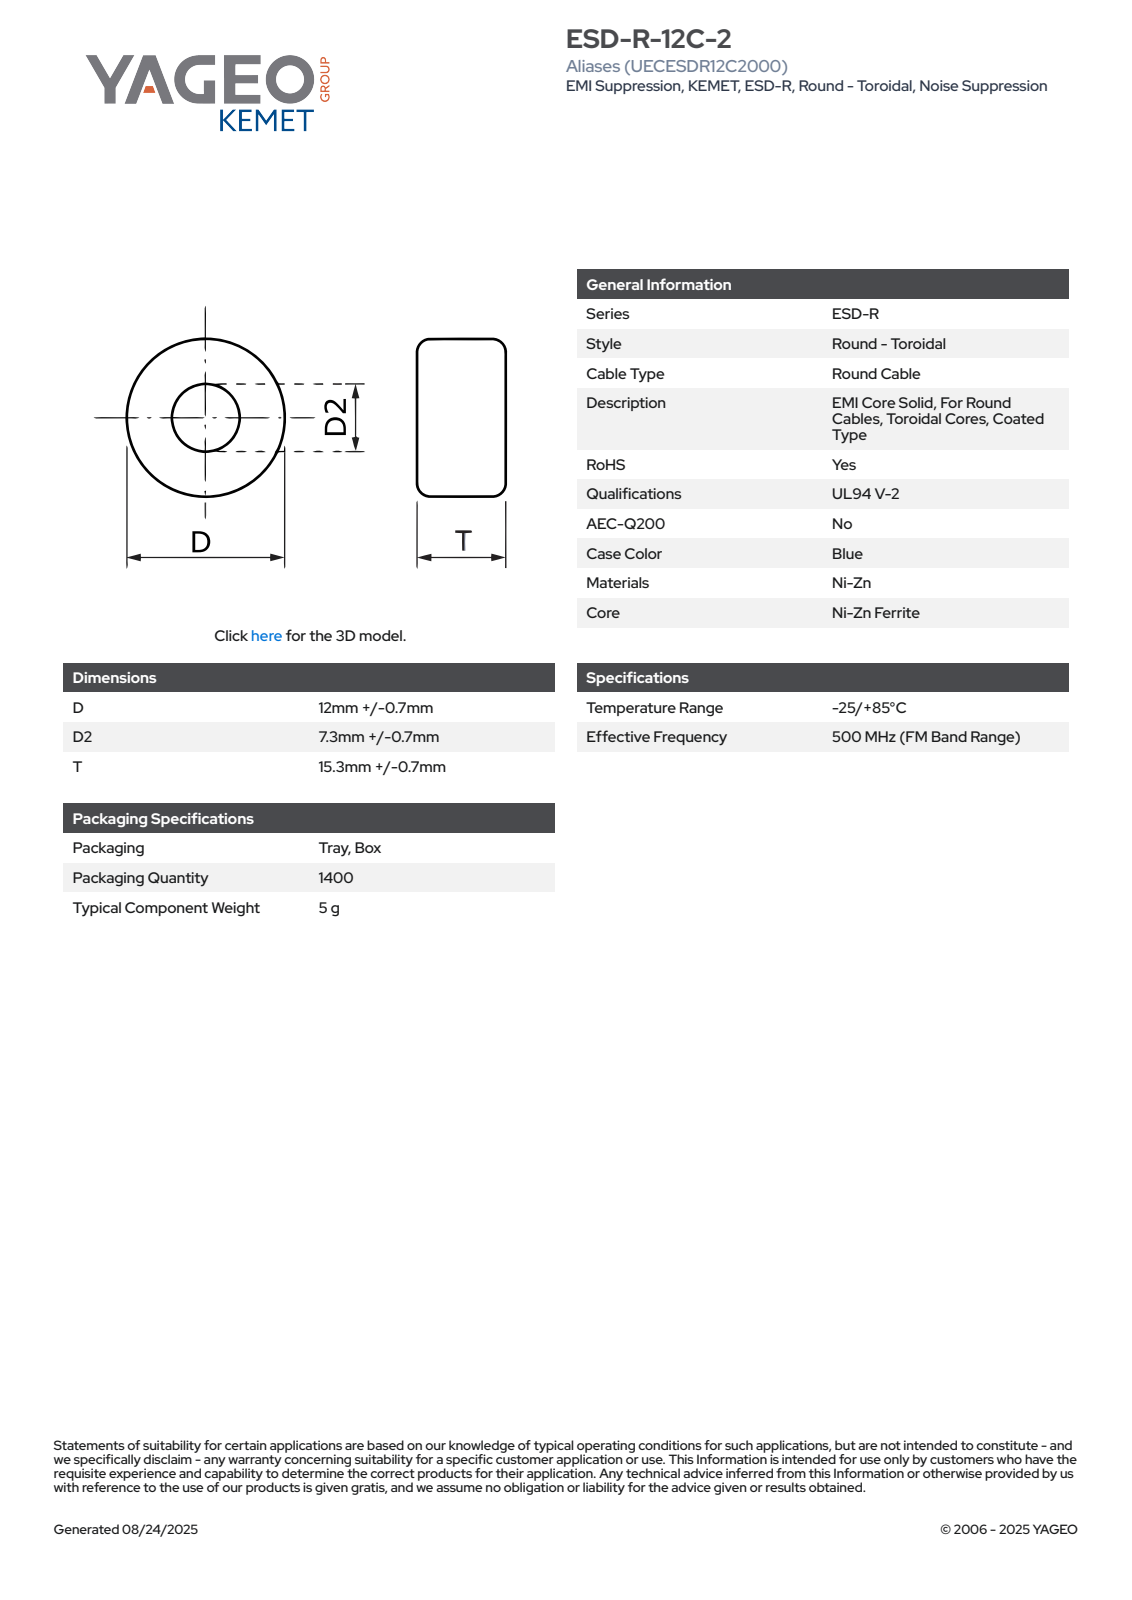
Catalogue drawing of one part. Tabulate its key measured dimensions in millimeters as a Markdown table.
| quantity | value |
| --- | --- |
| part name | EC_KBC_D12.7D27.3T16 |
| STEP written by | SolidWorks 2021 (AUTOMOTIVE_DESIGN) |
| units | millimeters |
| bodies | 1 solid, 66 faces (24 planar, 7 cylindrical, 35 other) |
| overall size | 16 × 12.71 × 12.7 |
| volume | 1 355 mm³ |
| surface area | 1 163 mm² |
| round holes (diameter × count) | 7.3 × 1 |
| round bosses / shafts (diameter × count) | 12.7 × 1 |
| partial cylindrical surfaces (radius × count) | 6.36 × 1 |
| main face-to-face distances | 16, 7.15, 8.85, 1.7, 0.32, 7.47, 8.53, 1.38, 1.06, 8.21 |
